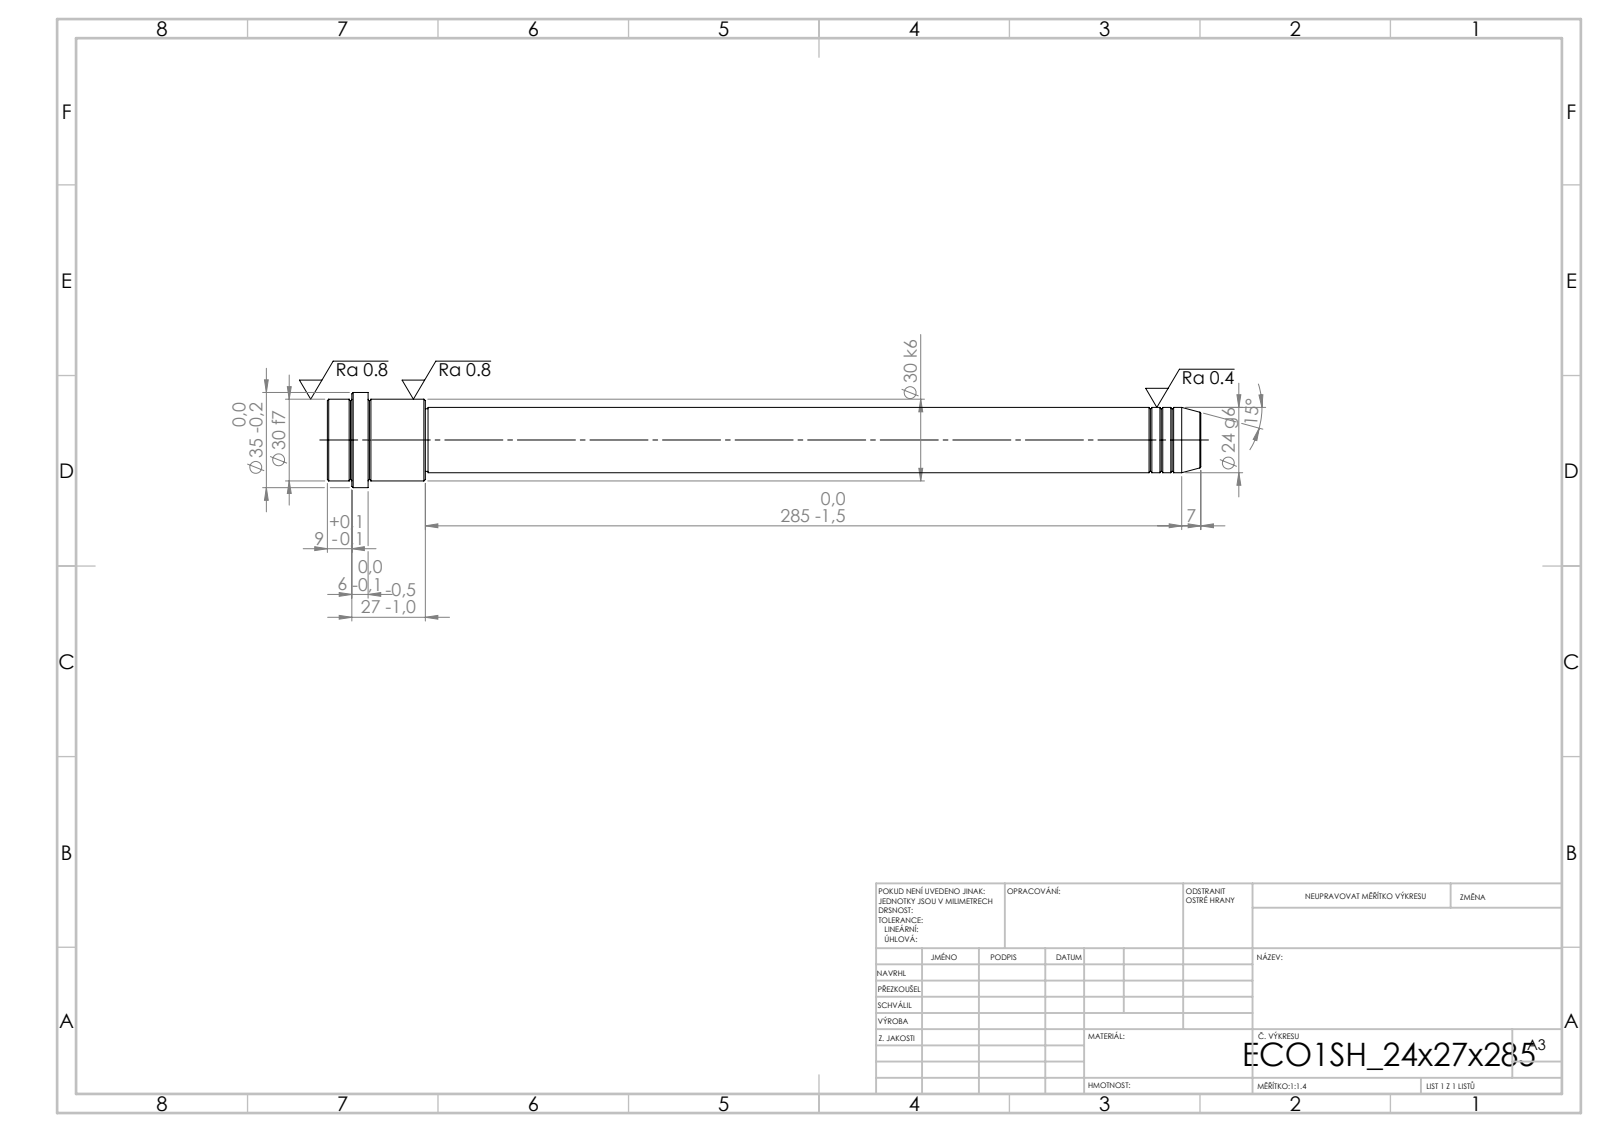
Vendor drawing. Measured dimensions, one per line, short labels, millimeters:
written by: SolidWorks 2019 (CONFIG_CONTROL_DESIGN)
unit: mm
bodies: 1 solid, 52 faces (6 planar, 16 cylindrical, 30 other)
size: 321 × 35 × 35
volume: 155 204 mm³; area: 26 941 mm²
bosses: 1× ⌀35, 1× ⌀30, 1× ⌀24, 1× ⌀23
face distances: 321, 306, 15, 285, 21, 36, 312, 27, 6, 9
